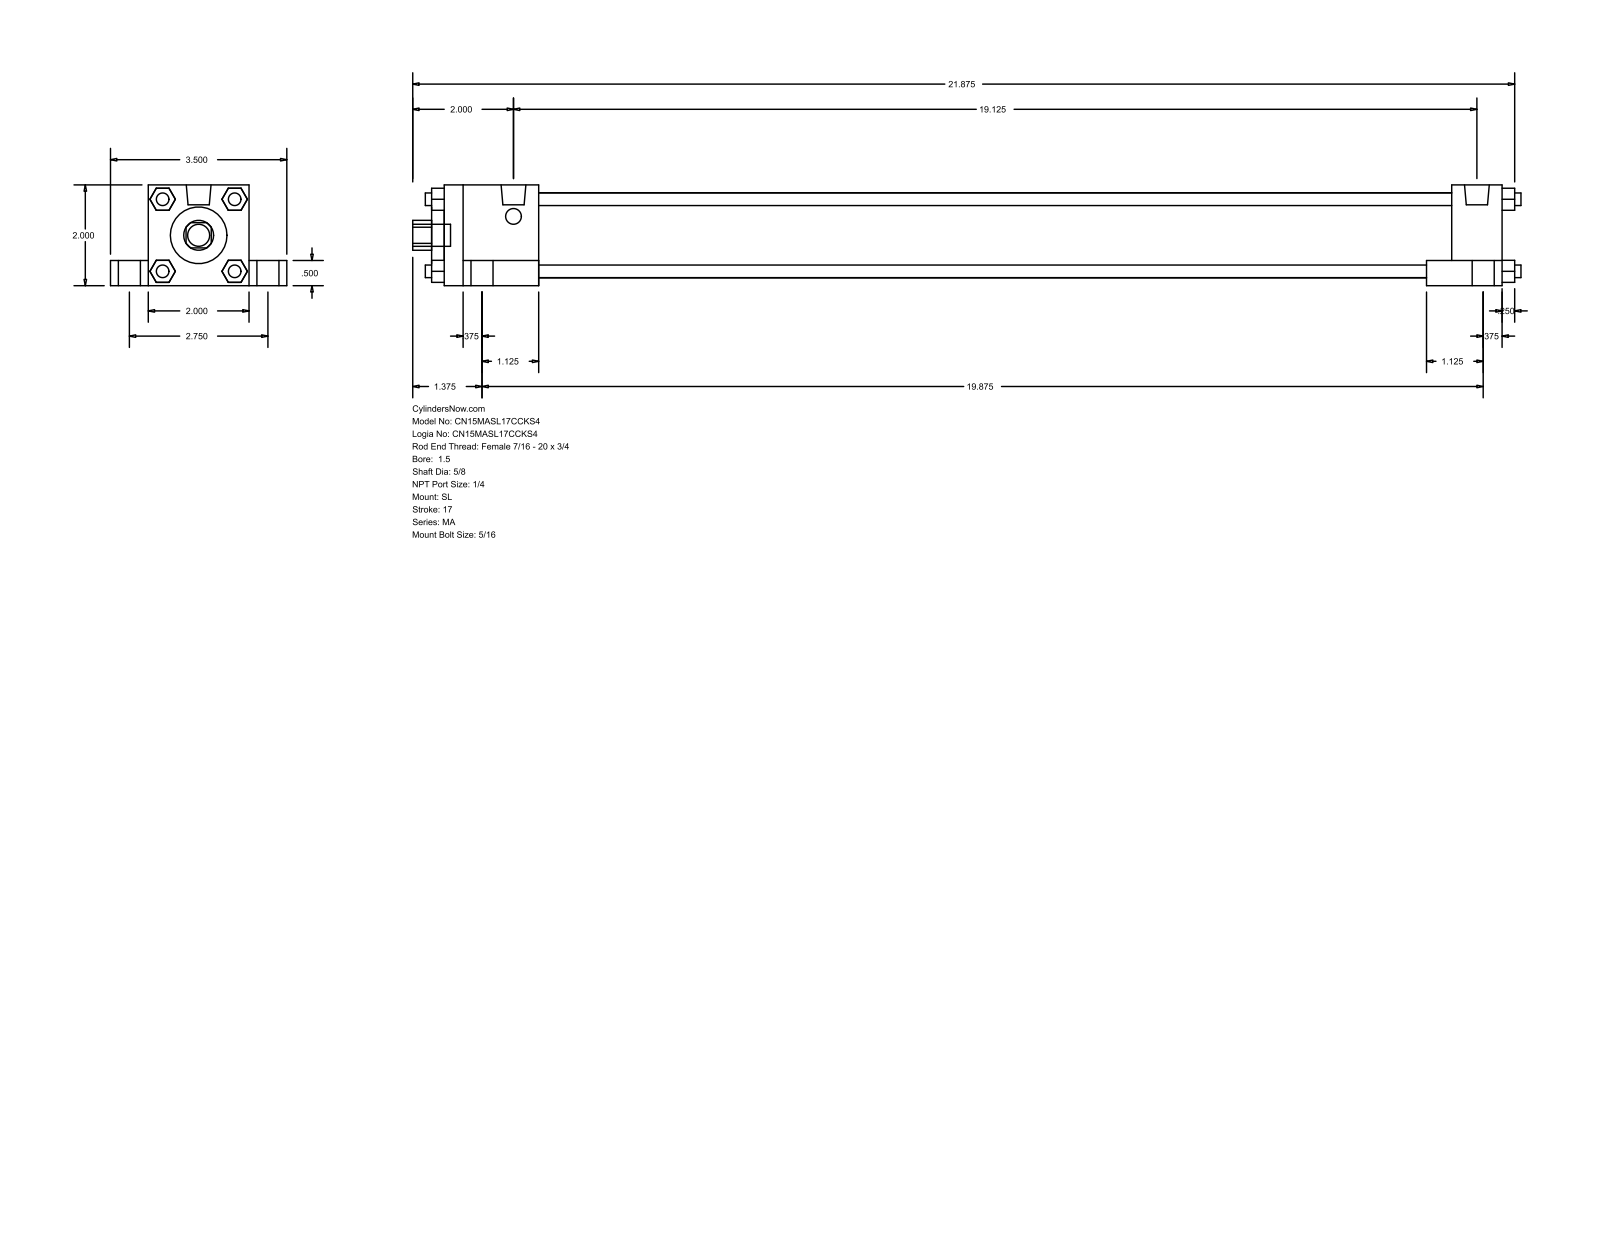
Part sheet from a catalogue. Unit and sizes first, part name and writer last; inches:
Units: inches
Overall size (bounding box): 22 × 3.5 × 2
Round holes (diameter × count): ⌀0.625 ×1, ⌀1.125 ×1, ⌀1.69 ×1
Round bosses / shafts (diameter × count): ⌀0.437 ×5, ⌀0.687 ×4, ⌀0.313 ×4, ⌀0.25 ×4, ⌀0.492 ×2
Partial cylindrical surfaces — rounded edges, fillets, slot ends (radius × count): R0.297 ×1
Main face-to-face distances: 2, 0.75, 1.5, 0.5, 2.75, 21, 0.25, 0.375, 21.25, 20
Bodies: 0 solids, 148 faces (112 planar, 36 cylindrical, 0 other)
Part name (STEP PRODUCT): MA_SL__0150_0.625
STEP written by: GSSL Pune (CONFIG_CONTROL_DESIGN)
